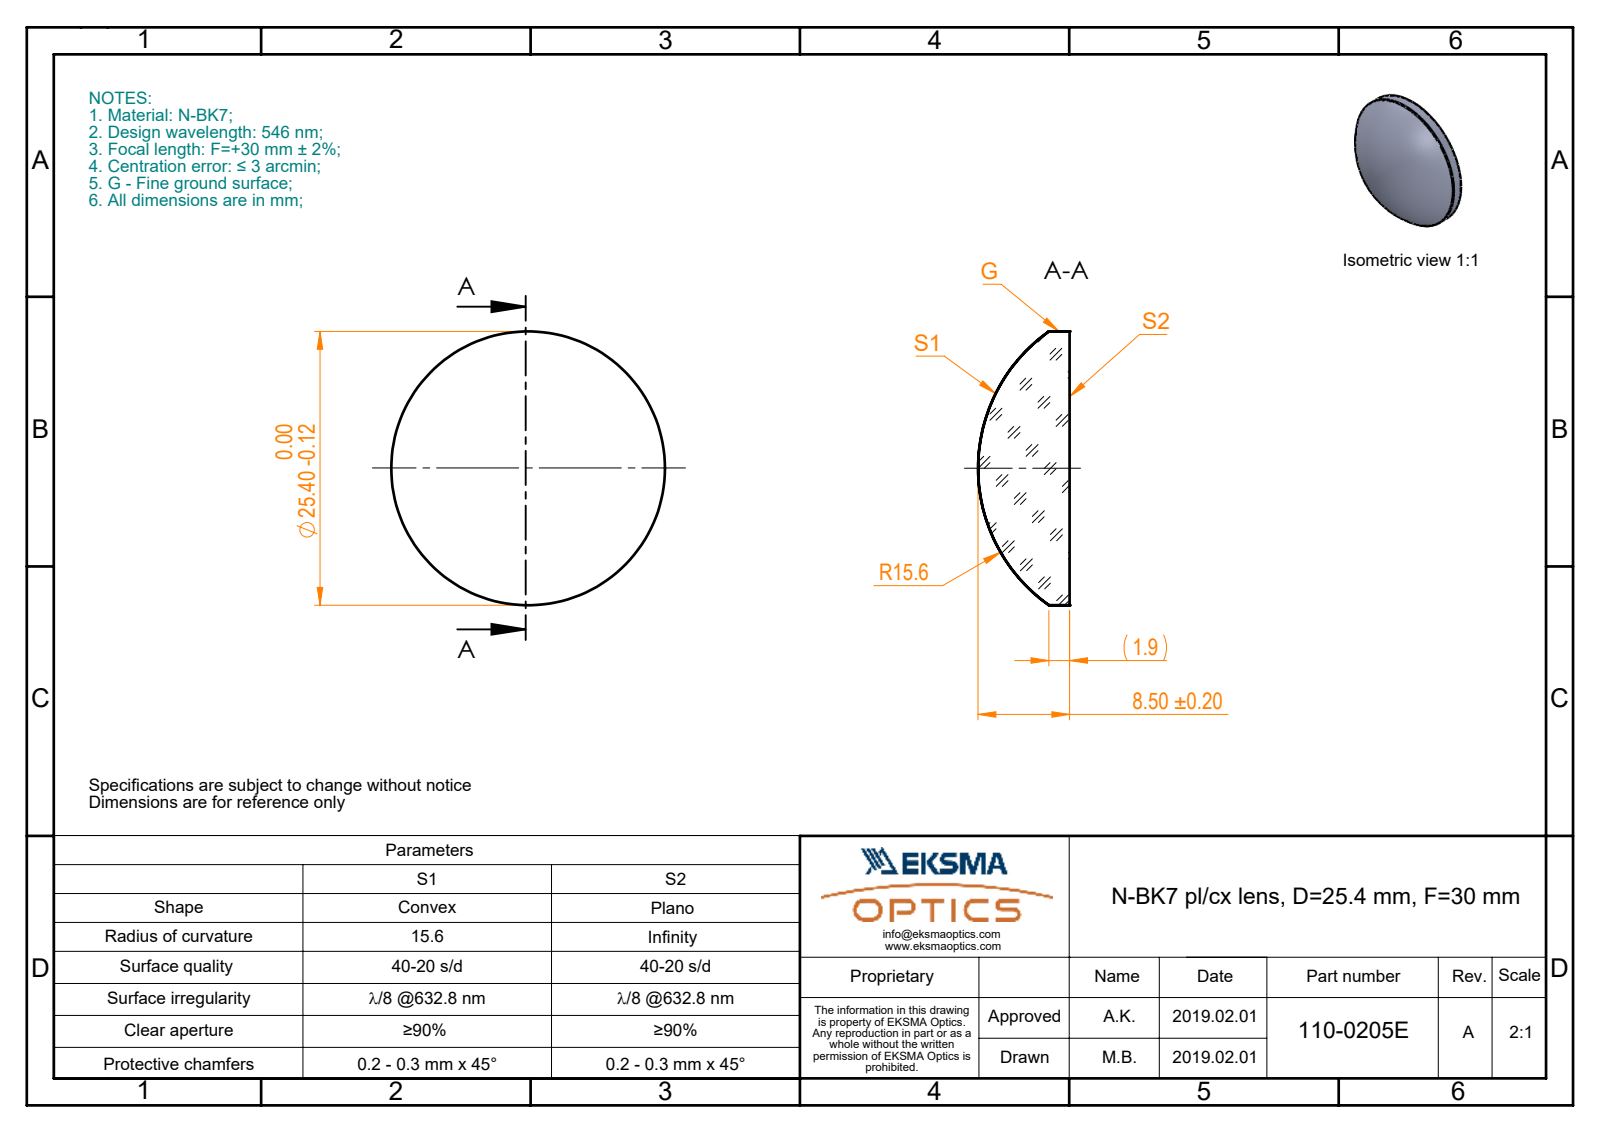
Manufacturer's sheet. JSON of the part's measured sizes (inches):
{"part_name": "110-0205E BK7 pl-cx 25.4 F30", "step_written_by": "SolidWorks 2017 (CONFIG_CONTROL_DESIGN)", "units": "inches", "bodies": {"solids": 1, "faces": 5, "planar": 1, "cylindrical": 2, "other": 2}, "overall_size": [1, 1, 0.335], "volume_in3": 0.17, "surface_area_in2": 2.02, "round_bosses_or_shafts": [[1, 1]]}
